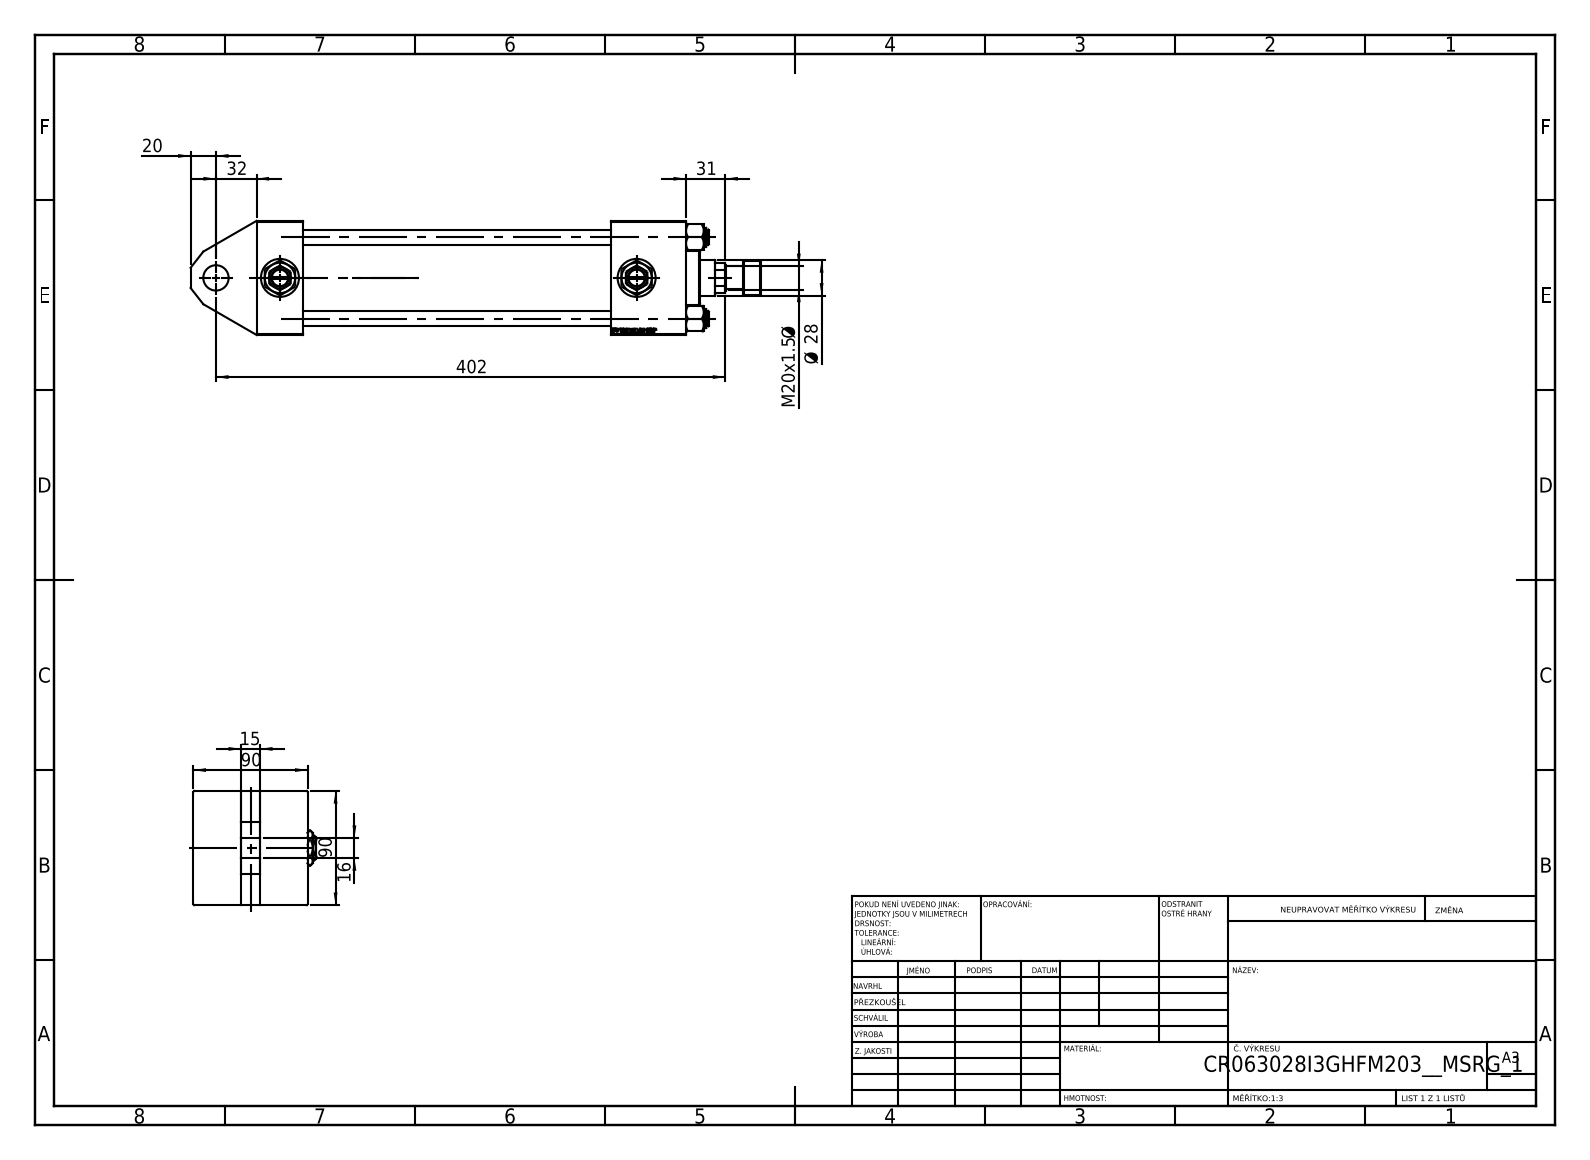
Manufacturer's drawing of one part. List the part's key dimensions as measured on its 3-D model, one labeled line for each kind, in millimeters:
Part name (STEP PRODUCT): V215_VC_A; NUT_M5_I; V215CR_VCP_I; V215CR_ROD_END_F (+3 more)
STEP written by: SolidWorks 2019 (CONFIG_CONTROL_DESIGN)
Units: millimetres
Bodies: 14 solids, 1194 faces (554 planar, 96 cylindrical, 544 other)
Overall size (bounding box): 450 × 97 × 90
Volume: 1 315 000 mm³ · Surface area: 317 773 mm²
Round holes (diameter × count): ⌀12 ×4, ⌀7 ×2, ⌀20.96 ×2, ⌀30 ×2, ⌀18.5 ×1, ⌀20 ×1, ⌀28 ×1, ⌀31 ×1, ⌀50 ×1, ⌀60 ×1, ⌀63 ×1
Round bosses / shafts (diameter × count): ⌀15 ×4, ⌀69 ×1, ⌀42 ×1, ⌀27 ×1, ⌀18 ×1
Main face-to-face distances: 90, 37, 339, 302, 59, 37.5, 52.5, 280, 243, 310.3
Hole centre spacings: 45.47, 64.3, 90.93, 50.5, 281.5, 332
